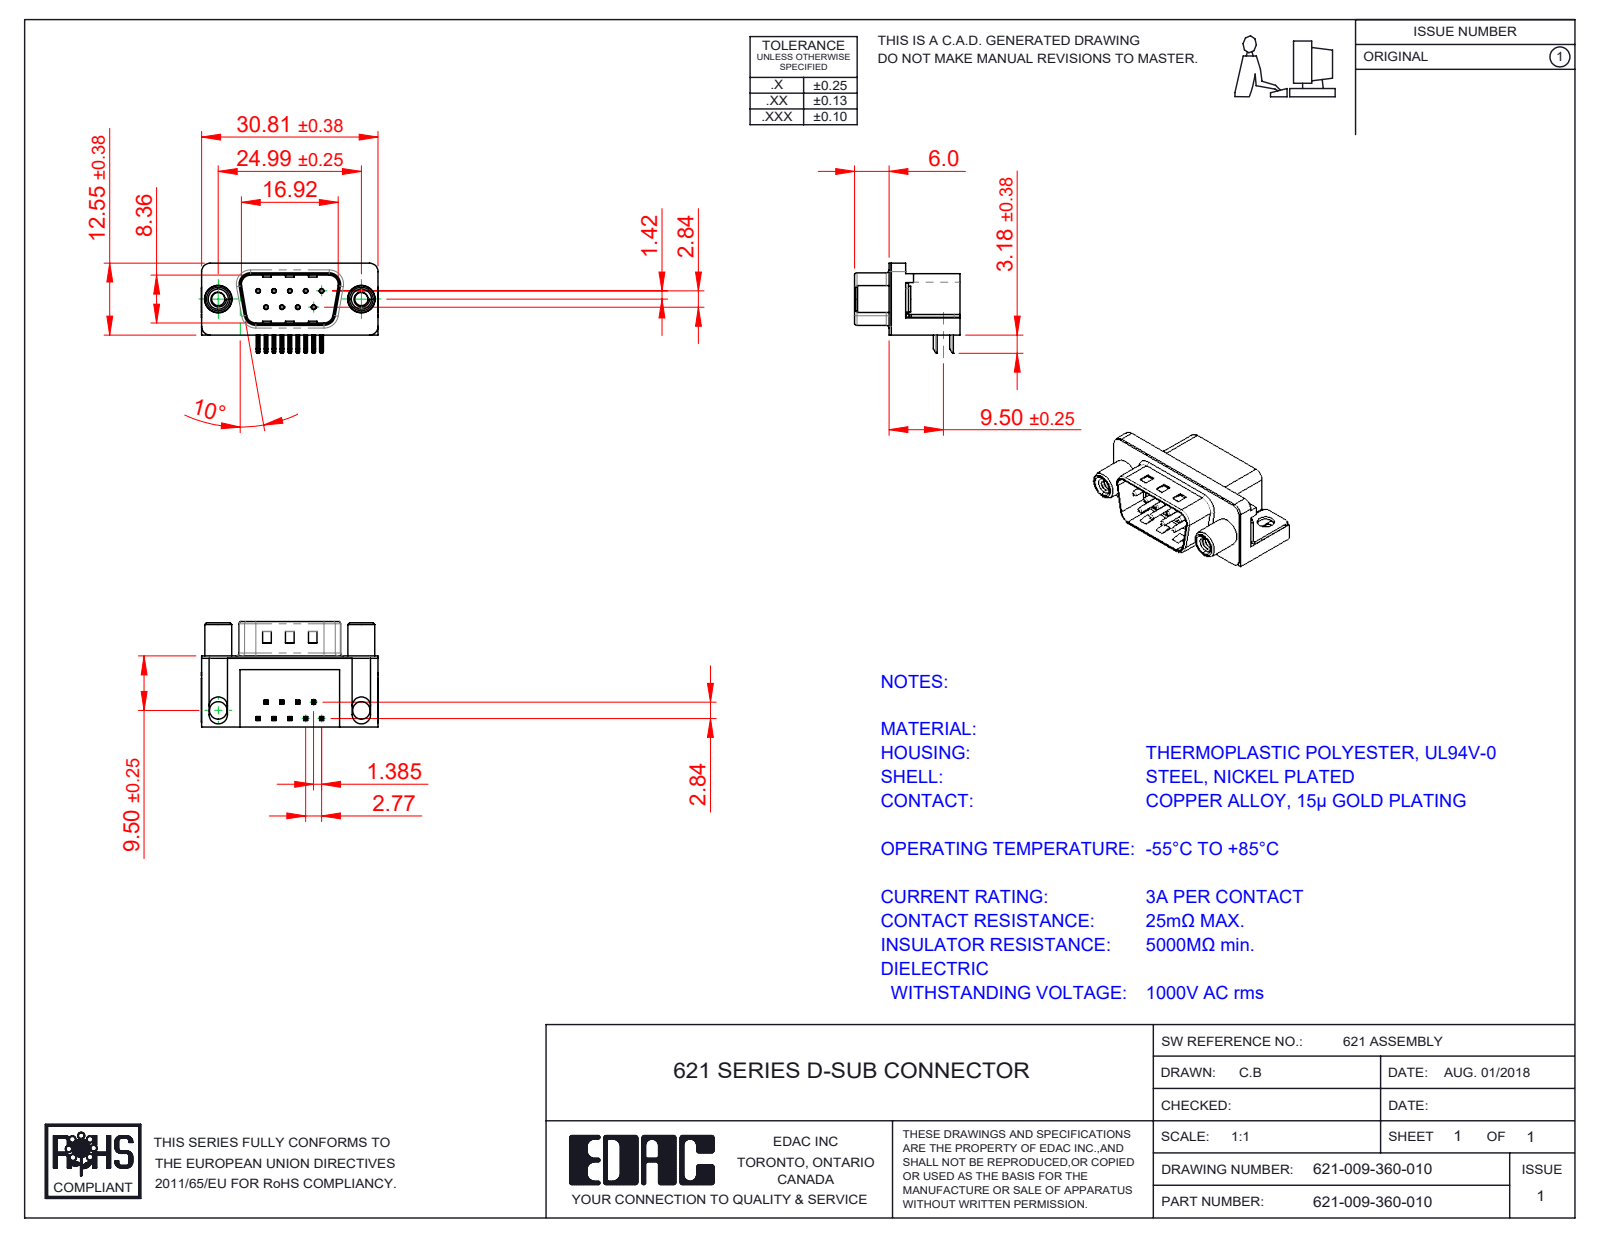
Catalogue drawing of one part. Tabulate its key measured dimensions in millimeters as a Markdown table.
| quantity | value |
| --- | --- |
| part name | 621 Housing_9 Socket; 621 Contact Top; 621 Thru Hole Board Mount; 621-009-360-010 (+3 more) |
| STEP written by | SolidWorks 2016 (CONFIG_CONTROL_DESIGN) |
| units | millimeters |
| bodies | 15 solids, 983 faces (563 planar, 323 cylindrical, 97 other) |
| overall size | 30.89 × 18.4 × 15.73 |
| volume | 3 334 mm³ |
| surface area | 4 607 mm² |
| round holes (diameter × count) | 0.35 × 9, 0.8 × 9, 2.3 × 2, 3.05 × 2, 3.1 × 2, 4 × 2, 4.8 × 2, 5 × 2 |
| round bosses / shafts (diameter × count) | 0.75 × 9, 4.9 × 2, 4.7 × 2, 4.5 × 2, 3.85 × 2 |
| partial cylindrical surfaces (radius × count) | 0.25 × 36, 0.12 × 18, 1 × 16, 0.5 × 9, 1.5 × 8, 1.6 × 8, 0.9 × 4, 2 × 4 |
| main face-to-face distances | 0.4, 12, 12.4, 10.35, 2.9, 9.5, 2.5, 0.5, 2.1, 0.35 |
| hole center spacings | 3.16, 2.77, 5.54, 5.03, 5.04, 8.31, 7.48, 7.49 |
